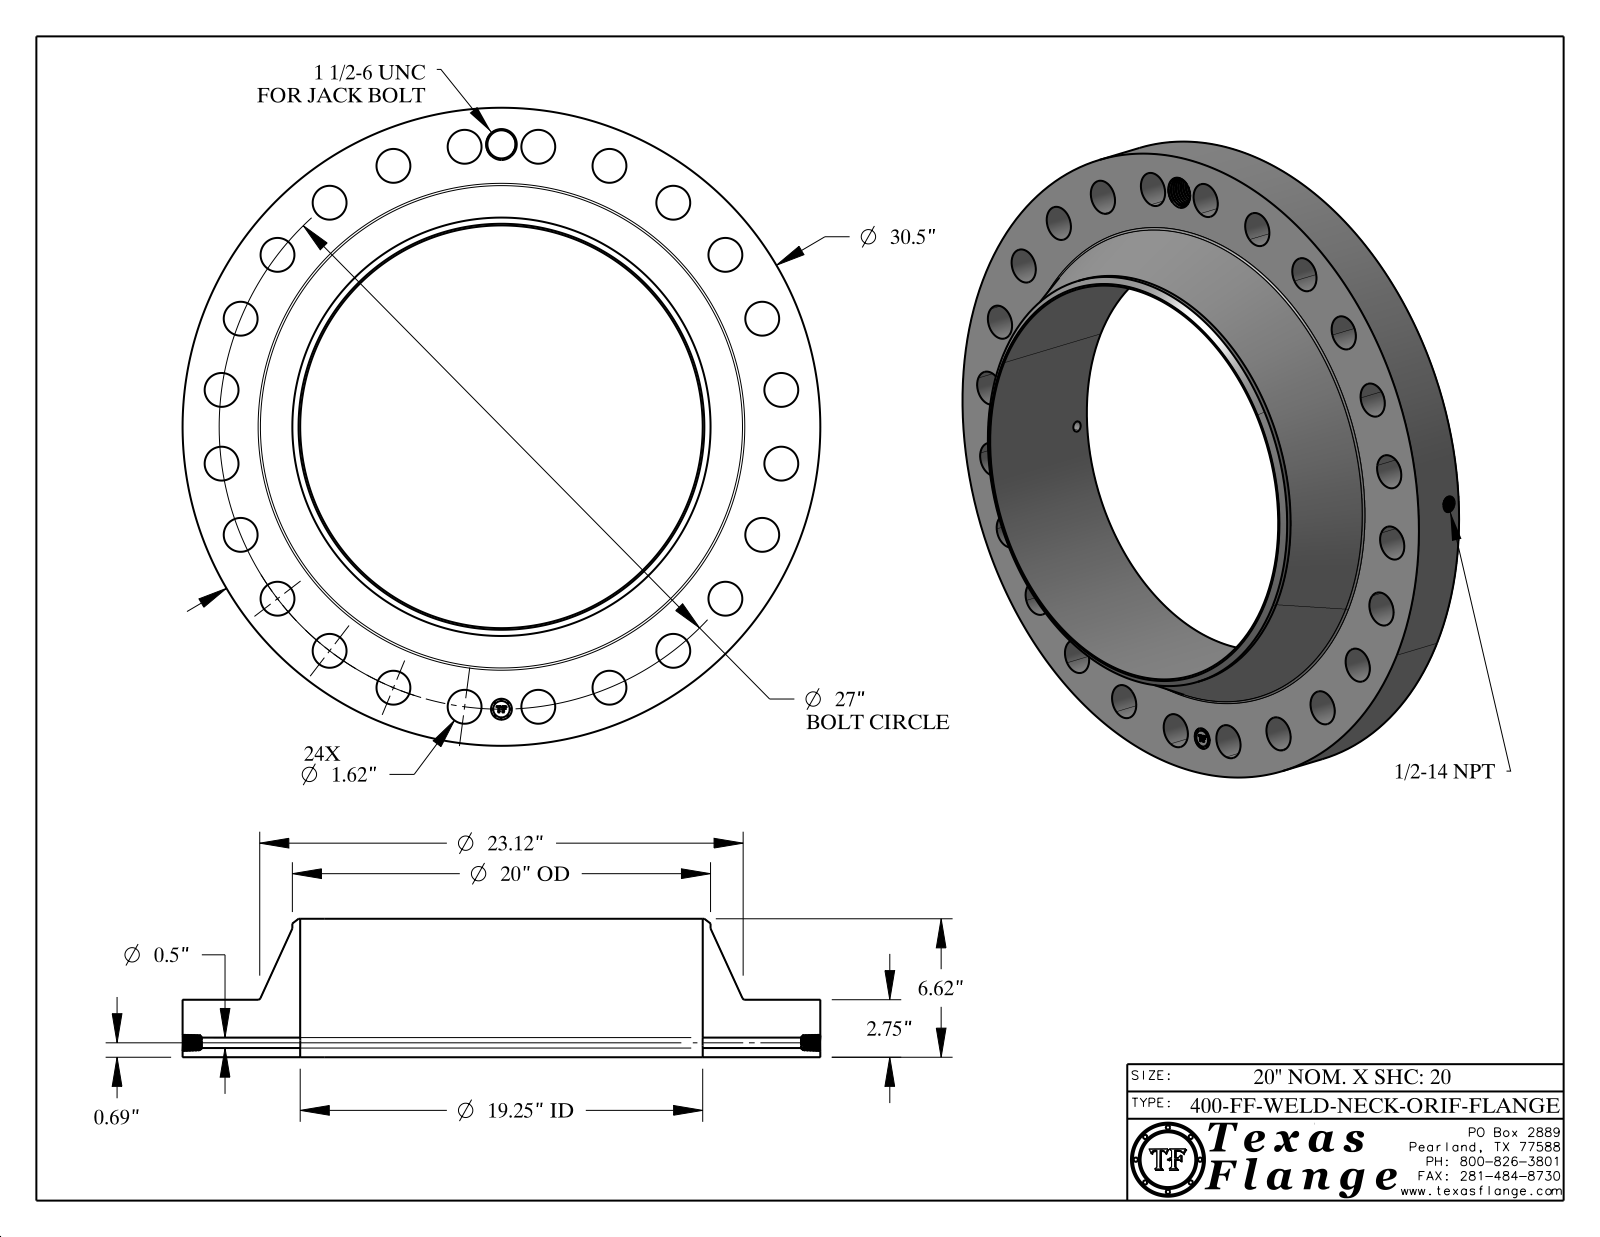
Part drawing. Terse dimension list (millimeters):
name: 400-FF-WELD-NECK
written by: CATIA V5 STEP AP214 (AUTOMOTIVE_DESIGN)
unit: mm
bodies: 1 solid, 807 faces (368 planar, 127 cylindrical, 312 other)
size: 774.7 × 774.7 × 168.1
volume: 21 780 000 mm³; area: 1 278 000 mm²
holes: 24× ⌀41.1, 1× ⌀12.7, 1× ⌀17.1, 1× ⌀25.4, 1× ⌀34.1, 1× ⌀489
bosses: 8× ⌀1.5, 1× ⌀774.7, 1× ⌀508, 1× ⌀20
face distances: 69.9, 168.1, 98.3, 69.5, 0.4, 98.7, 7.6, 7.4, 1.4, 6.3
hole spacings: 342.9, 593.9, 633.6, 544.1, 89.5, 177.5, 484.9, 662.4
